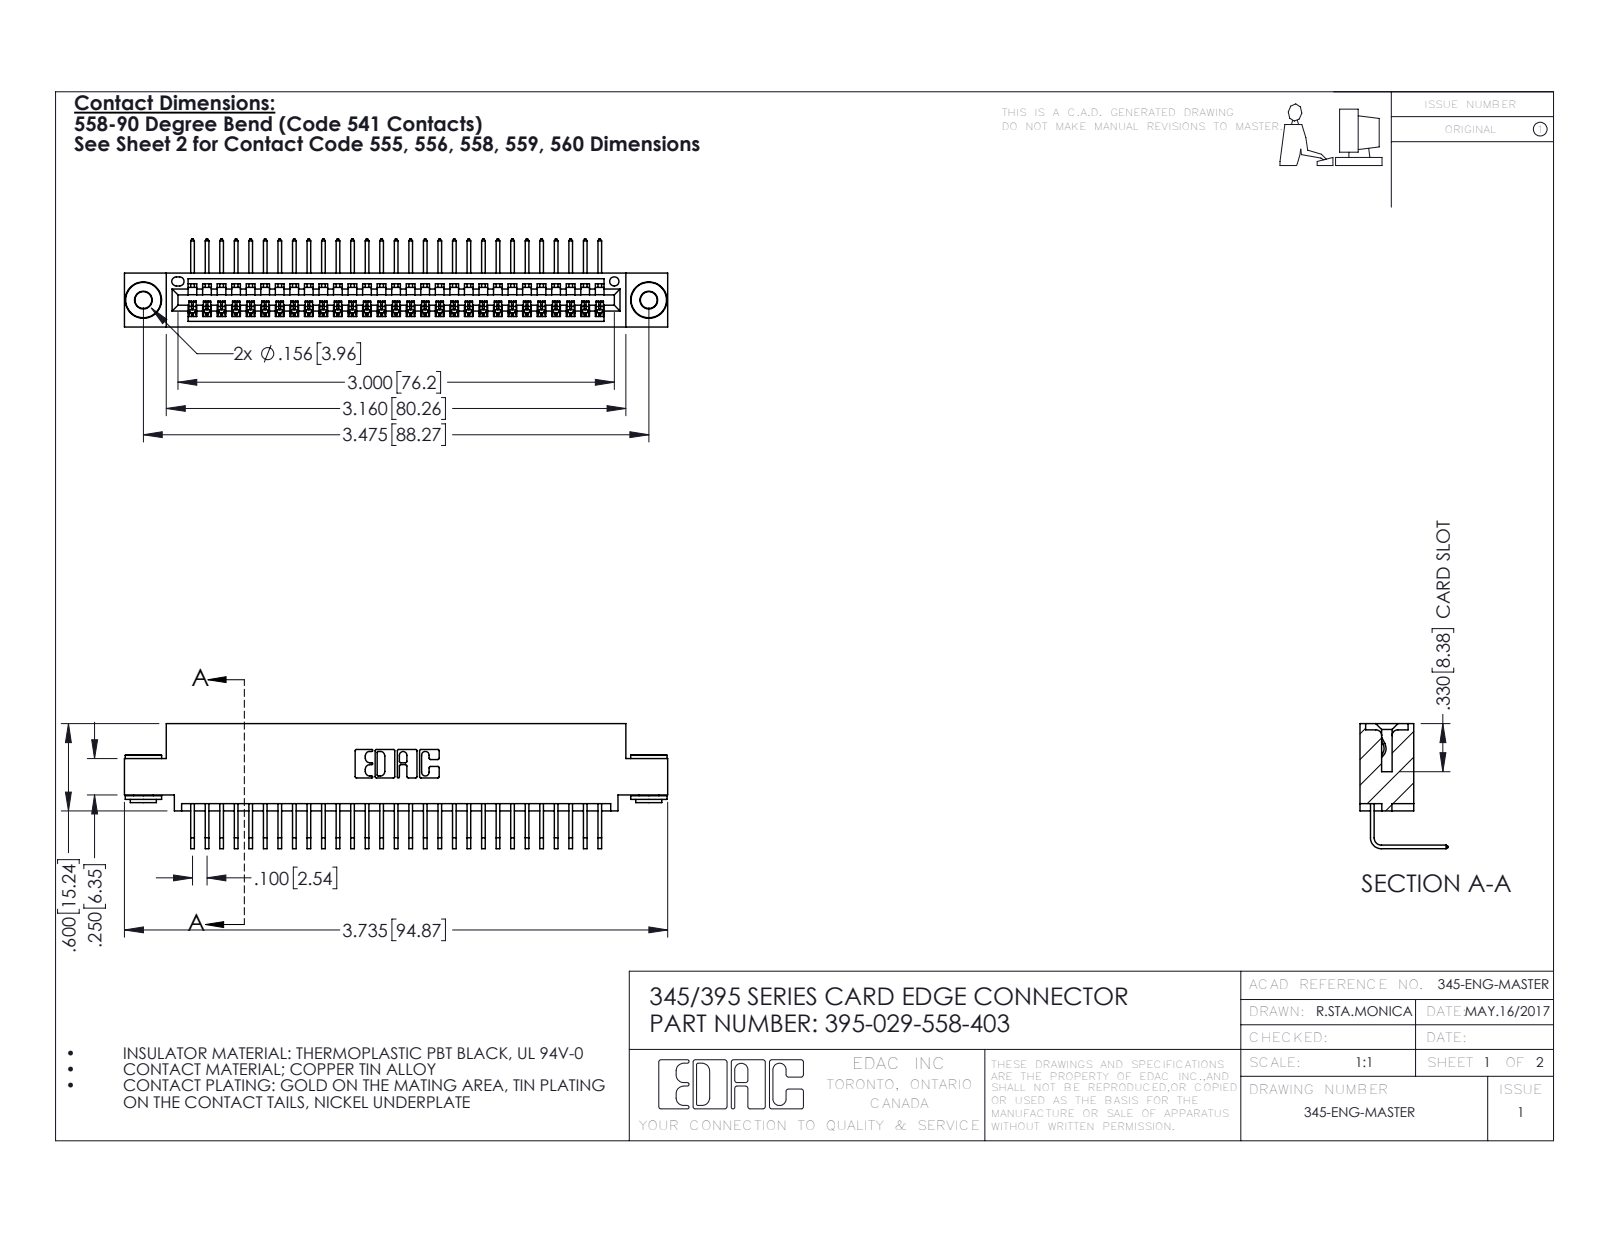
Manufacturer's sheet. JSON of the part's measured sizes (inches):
{"part_name": "395-029-558-403; 345 Part_0.110 Offset - 0.156 Dia-TH; 345-292-001_558 Tail - 2; 345-250-002_345-250-002-102", "step_written_by": "SolidWorks 2016 (CONFIG_CONTROL_DESIGN)", "units": "inches", "bodies": {"solids": 32, "faces": 1908, "planar": 1312, "cylindrical": 588, "other": 8}, "overall_size": [3.735, 0.859, 0.605], "volume_in3": 0.546, "surface_area_in2": 19.49, "round_holes": [[0.116, 2], [0.156, 2], [0.064, 1]], "round_bosses_or_shafts": [[0.25, 2], [0.18, 2], [0.136, 2]], "partial_cylinders_radius": [[0.006, 58], [0.01, 22], [0.007, 6], [0.031, 6], [0.026, 3], [0.031, 2], [0.04, 2], [0.014, 1]], "face_to_face_distances": [0.072, 0.298, 0.37, 0.2, 0.025, 0.098, 0.272, 0.225, 0.149, 0.072], "hole_center_spacings": [0.27, 3.24, 3.475]}
